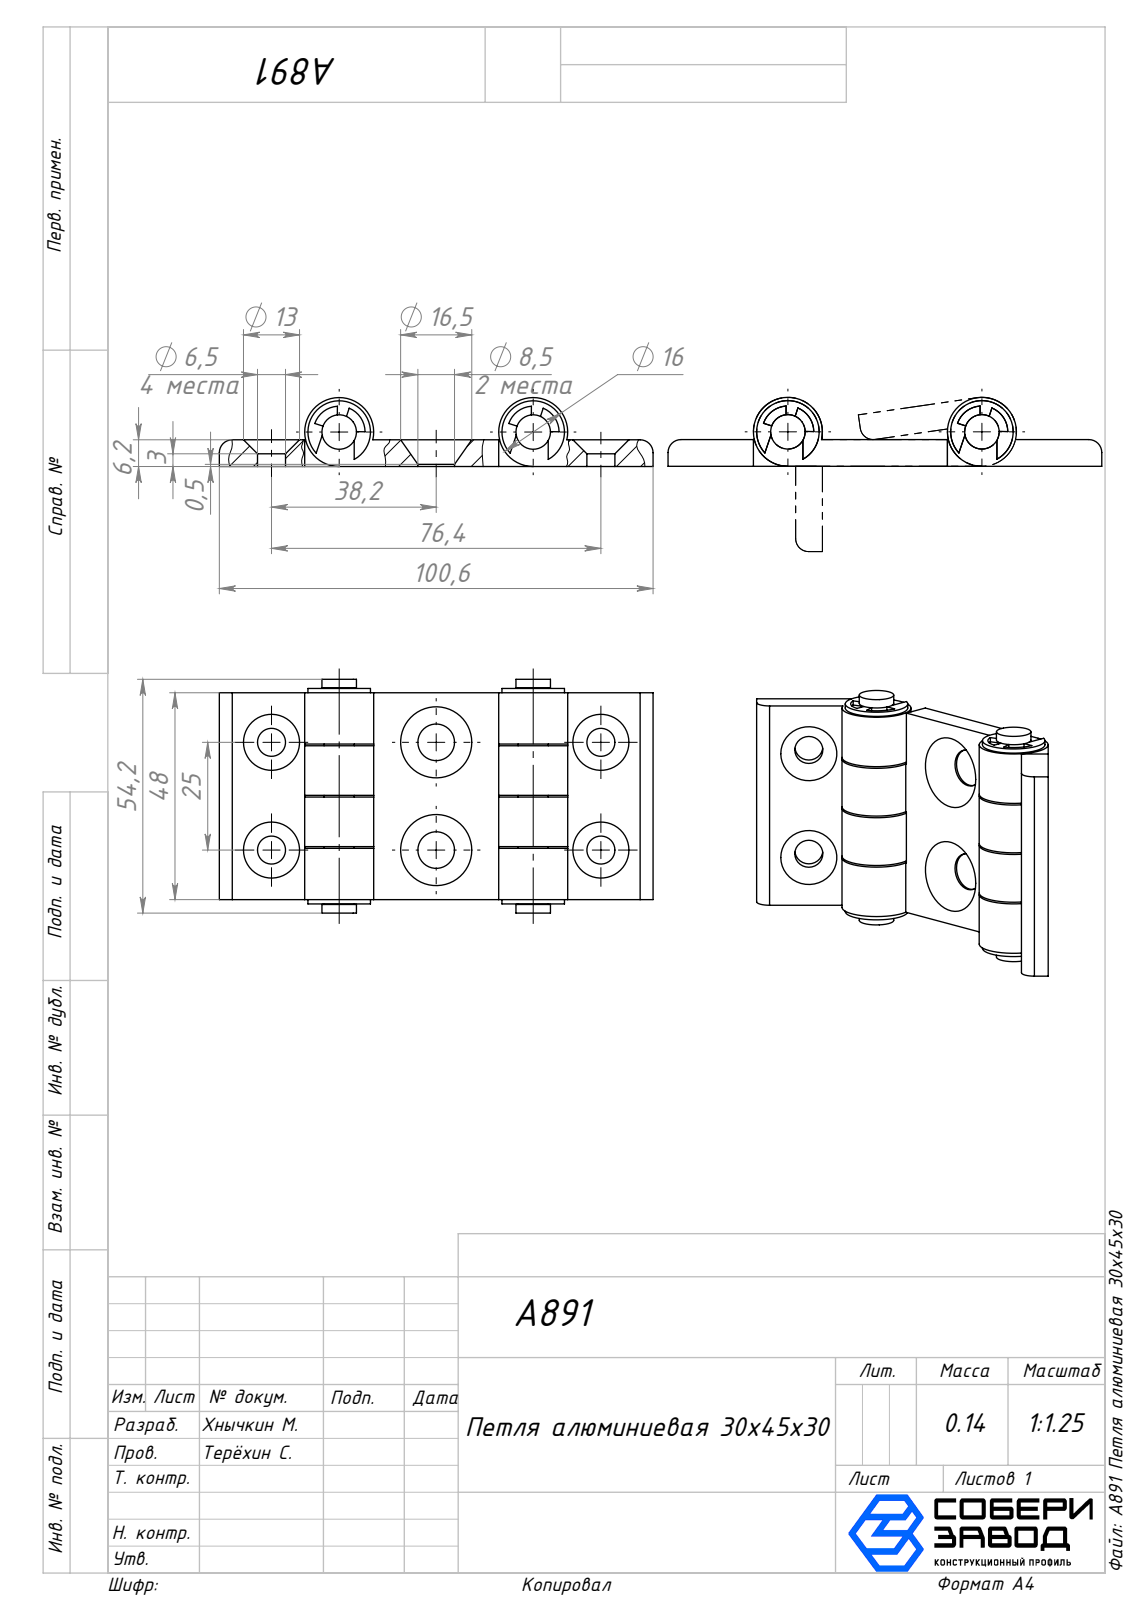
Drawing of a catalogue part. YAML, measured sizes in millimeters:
part_name: "A821 Палец_01; A821 Кольцо_00; A821 Петля, часть 30 серии_00; A821 Сред петля_00 (+1 more)"
step_written_by: "SolidWorks 2025 (AUTOMOTIVE_DESIGN)"
units: millimeters
bodies: {solids: 9, faces: 180, planar: 74, cylindrical: 94, other: 12}
overall_size: [100.58, 54.25, 16]
volume: 38339
surface_area: 21494
round_holes:
  - {diameter: 6.5, count: 4}
  - {diameter: 7, count: 2}
  - {diameter: 8.5, count: 2}
round_bosses_or_shafts:
  - {diameter: 16, count: 2}
  - {diameter: 8, count: 2}
partial_cylinders:
  - {radius: 3, count: 2}
  - {radius: 6, count: 2}
  - {radius: 7.25, count: 2}
face_to_face_distances: [11.9, 6.2, 12.3, 23.8, 24.2, 0.4, 48, 36.1, 35.7, 11.5]
hole_center_spacings: [38.19, 45.65, 25, 76.38, 80.37, 44.98]
